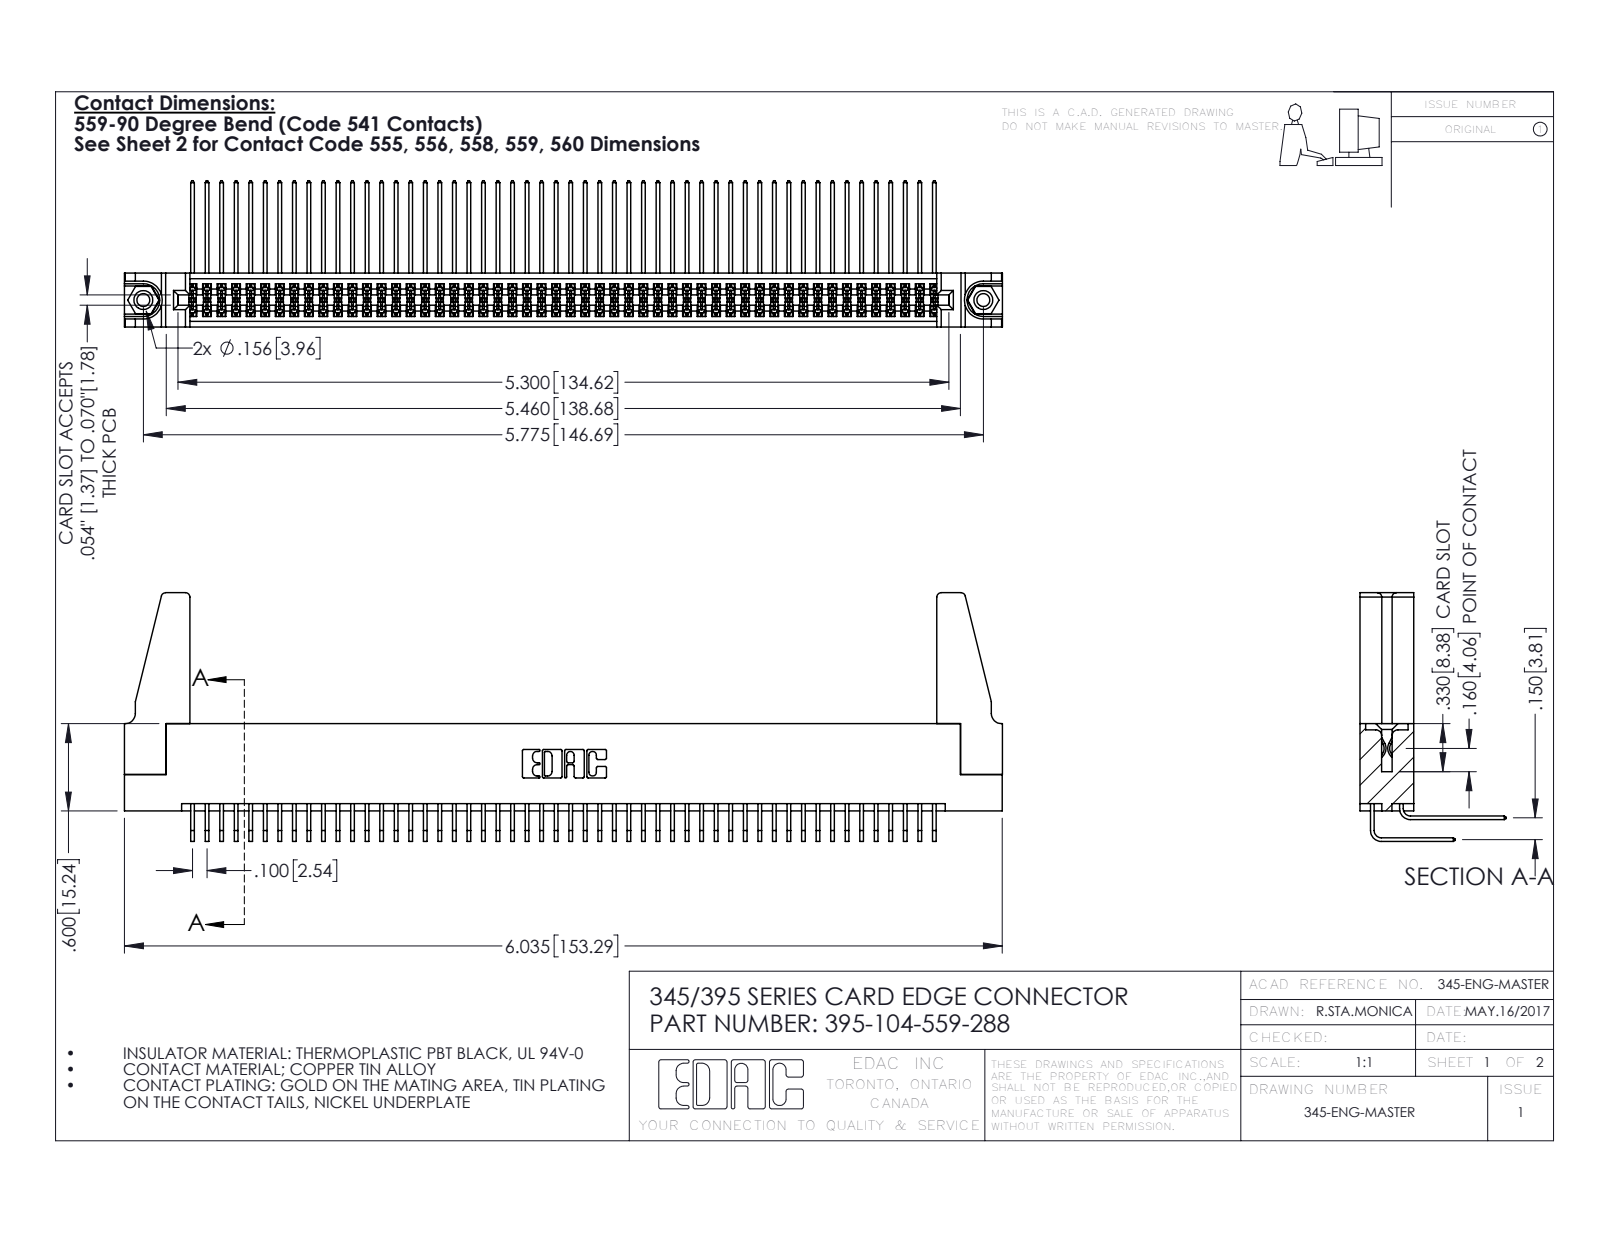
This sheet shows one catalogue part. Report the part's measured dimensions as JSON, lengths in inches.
{"part_name": "345-220-078_345-220-088; 345-292-001_558 559 Tail - 1; 345-250-001_345-250-001-102; 345 Part_Flush Mounting Lugs - 0.156 Dia-TH (+2 more)", "step_written_by": "SolidWorks 2016 (CONFIG_CONTROL_DESIGN)", "units": "inches", "bodies": {"solids": 109, "faces": 5658, "planar": 3792, "cylindrical": 1850, "other": 16}, "overall_size": [6.036, 1.709, 1.005], "volume_in3": 1.15, "surface_area_in2": 45.22, "round_holes": [[0.089, 2], [0.125, 2], [0.156, 2], [0.064, 1]], "round_bosses_or_shafts": [[0.155, 2]], "partial_cylinders_radius": [[0.006, 157], [0.01, 22], [0.03, 8], [0.007, 6], [0.031, 6], [0.026, 3], [0.014, 2], [0.019, 2]], "face_to_face_distances": [0.072, 0.298, 0.37, 0.2, 0.098, 0.272, 0.025, 0.225, 0.175, 0.15], "hole_center_spacings": [0.27, 5.539, 5.775]}
